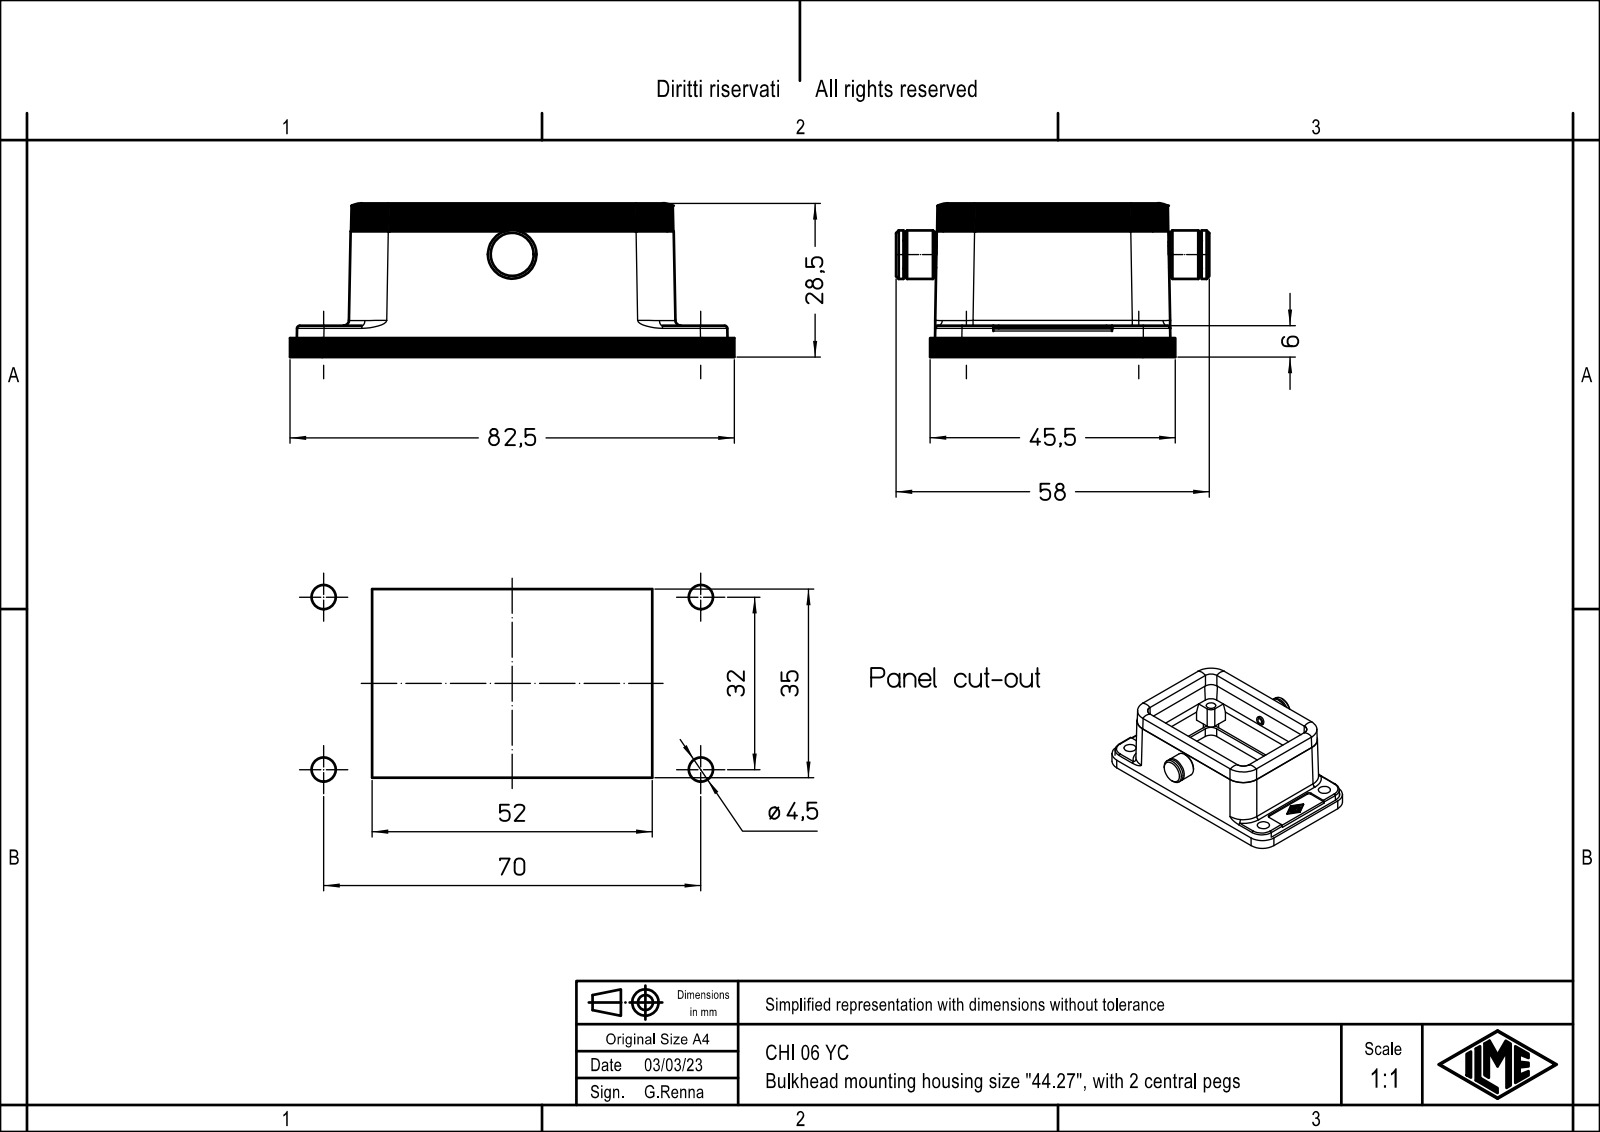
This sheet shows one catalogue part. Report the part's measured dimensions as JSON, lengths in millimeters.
{"part_name": "CHI_06_YC", "step_written_by": "Creo Elements/Direct Modeling 18.0B 02-Dec-2011 (C) Parametric Technology GmbH (AUTOMOTIVE_DESIGN)", "units": "millimeters", "bodies": {"solids": 1, "faces": 209, "planar": 98, "cylindrical": 99, "other": 12}, "overall_size": [82.5, 58.5, 29], "volume_mm3": 26392, "surface_area_mm2": 16565, "round_holes": [[2.46, 4], [3.1, 4], [4.4, 4], [4.5, 4]], "round_bosses_or_shafts": [[9, 1]], "partial_cylinders_radius": [[0.33, 15], [6, 8], [1, 6], [1.5, 4], [2, 4], [2.5, 4], [3, 4], [4, 4]], "face_to_face_distances": [3, 40.5, 4, 0.75, 1, 40.75, 57, 29, 3.25, 43.5], "hole_center_spacings": [13.29, 32.47, 57.07, 64.3, 27, 32.5, 44, 51.62]}
